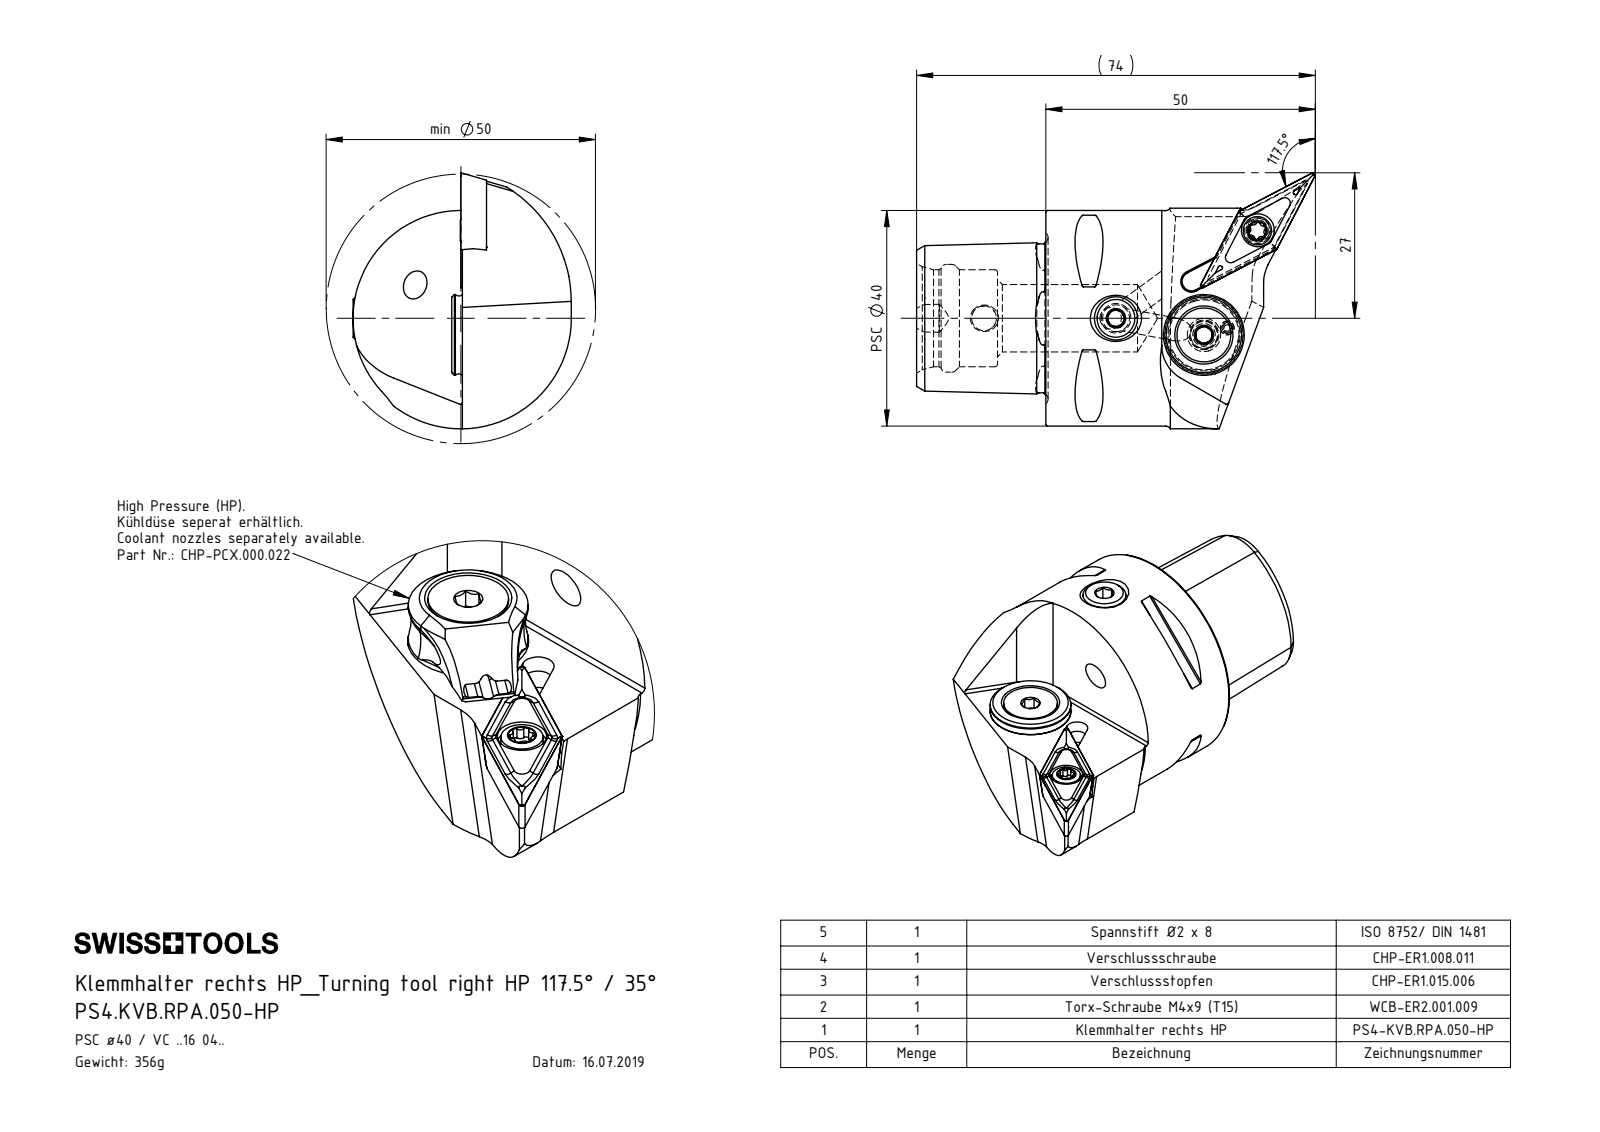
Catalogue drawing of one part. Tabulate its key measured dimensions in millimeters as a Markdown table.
| quantity | value |
| --- | --- |
| part name | WCB-ER2.001.009_A; PS4-KVB.RPA.050-HP_A_Fertigbearbeitung; CHP-ER1.015.006_A; DIN 7991 - M5x15 (+6 more) |
| STEP written by | SolidWorks 2017 (AUTOMOTIVE_DESIGN) |
| units | millimeters |
| bodies | 8 solids, 392 faces (94 planar, 100 cylindrical, 198 other) |
| overall size | 74 × 47.5 × 40.73 |
| volume | 44 970 mm³ |
| surface area | 15 088 mm² |
| round holes (diameter × count) | 3.3 × 3, 1.2 × 1, 2 × 1, 2.5 × 1, 3 × 1, 4 × 1, 4.2 × 1, 4.4 × 1, 4.6 × 1, 5 × 1, 5.2 × 1, 6.1 × 1 |
| round bosses / shafts (diameter × count) | 40 × 1, 15 × 1, 13.4 × 1, 10 × 1, 8 × 1, 5.5 × 1, 5.25 × 1, 5 × 1 |
| partial cylindrical surfaces (radius × count) | 0.3 × 8, 0.34 × 6, 0.59 × 6, 7 × 3, 0.5 × 2, 1.75 × 1, 3 × 1, 20.5 × 1 |
| main face-to-face distances | 21.5, 4.5, 4.46, 24, 45.5, 15.52, 35.3, 15, 6.4, 6.36 |
| hole center spacings | 4.5, 17.6, 18.91, 19.01, 21.71, 21.74, 21.85, 23.5 |
